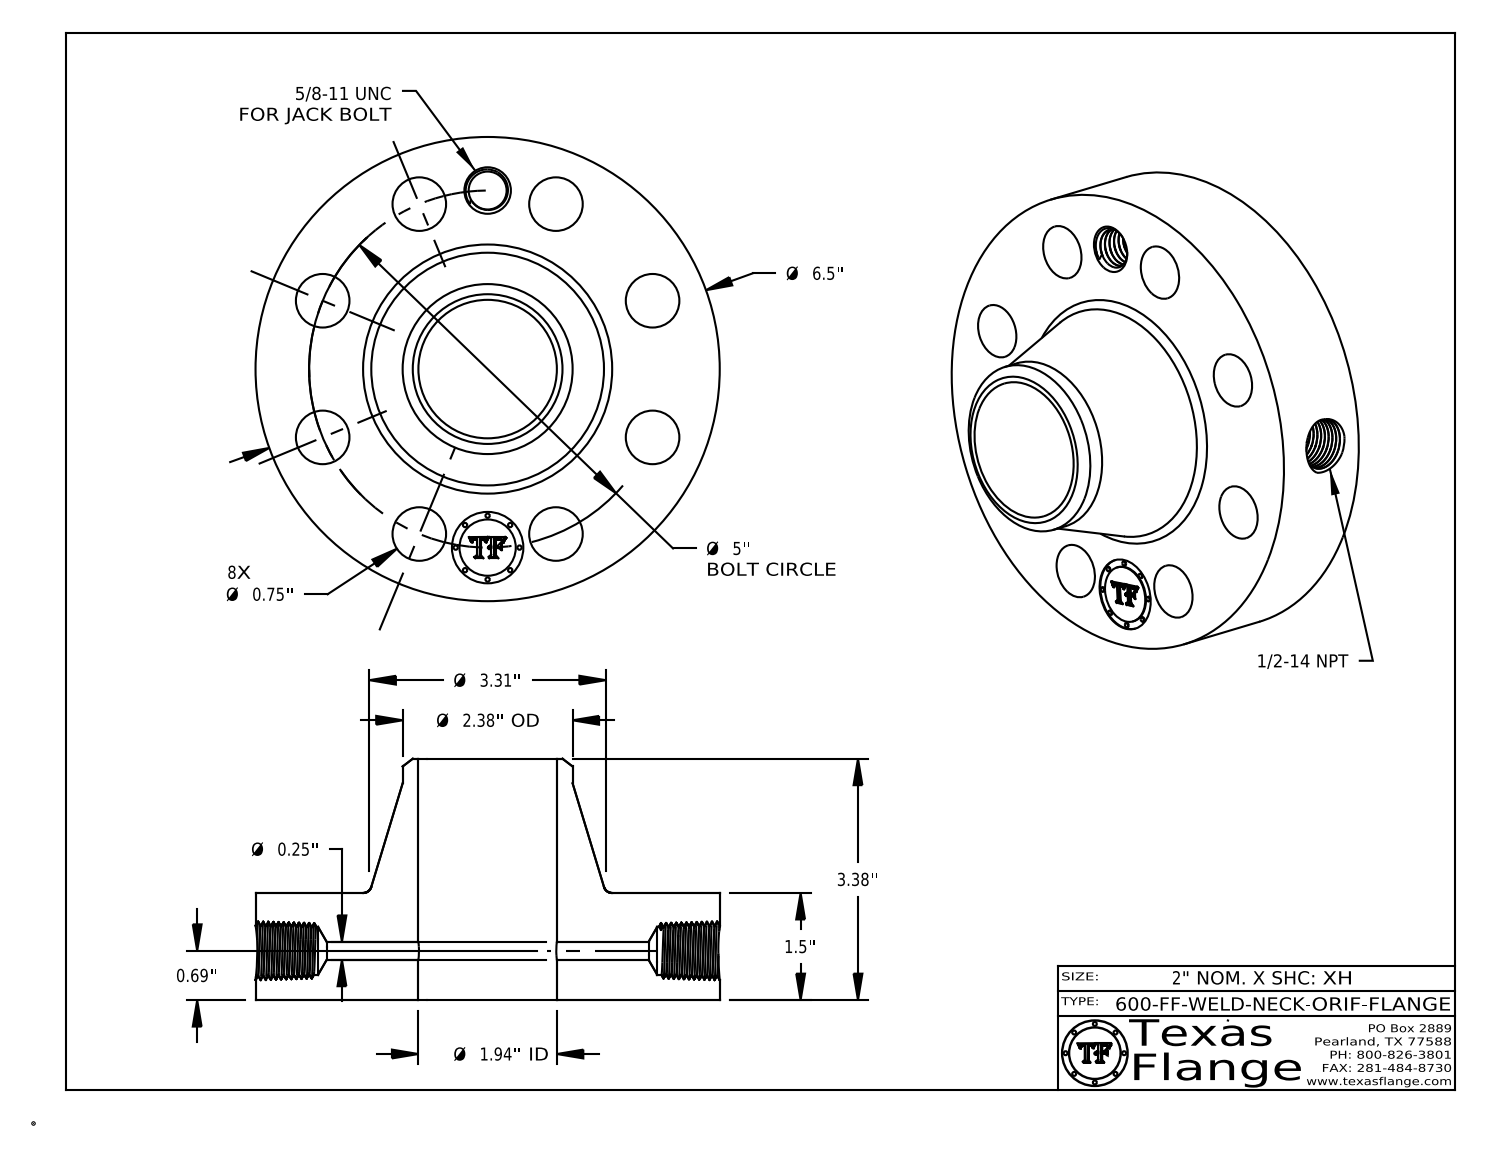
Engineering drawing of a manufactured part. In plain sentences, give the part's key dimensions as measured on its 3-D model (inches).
The part is named "600-FF-WELD-NECK". Its 3-D file was written by "CATIA V5 STEP AP214 (AUTOMOTIVE_DESIGN)". It is 1 solid with 775 faces: 368 planar, 93 cylindrical and 314 other. Overall it measures 6.5 by 6.5 by 3.38 inches. Its volume is 44.53 cubic inches and its surface area 157.2 square inches. Round holes: 8 of diameter 0.75, 1 of diameter 0.25, 1 of diameter 0.531, 1 of diameter 0.672, 1 of diameter 1, 1 of diameter 1.939. Round bosses or shafts: 8 of diameter 0.061, 1 of diameter 6.5, 1 of diameter 2.38, 1 of diameter 0.788. The main face-to-face distances are 1.5, 3.38, 1.88, 1.485, 0.015, 1.895, 0.298, 0.293, 0.054, 0.248. The hole center spacings are 2.5, 3.536, 4.62, 0.976, 1.913, 1.914, 2.778, 4.157.
